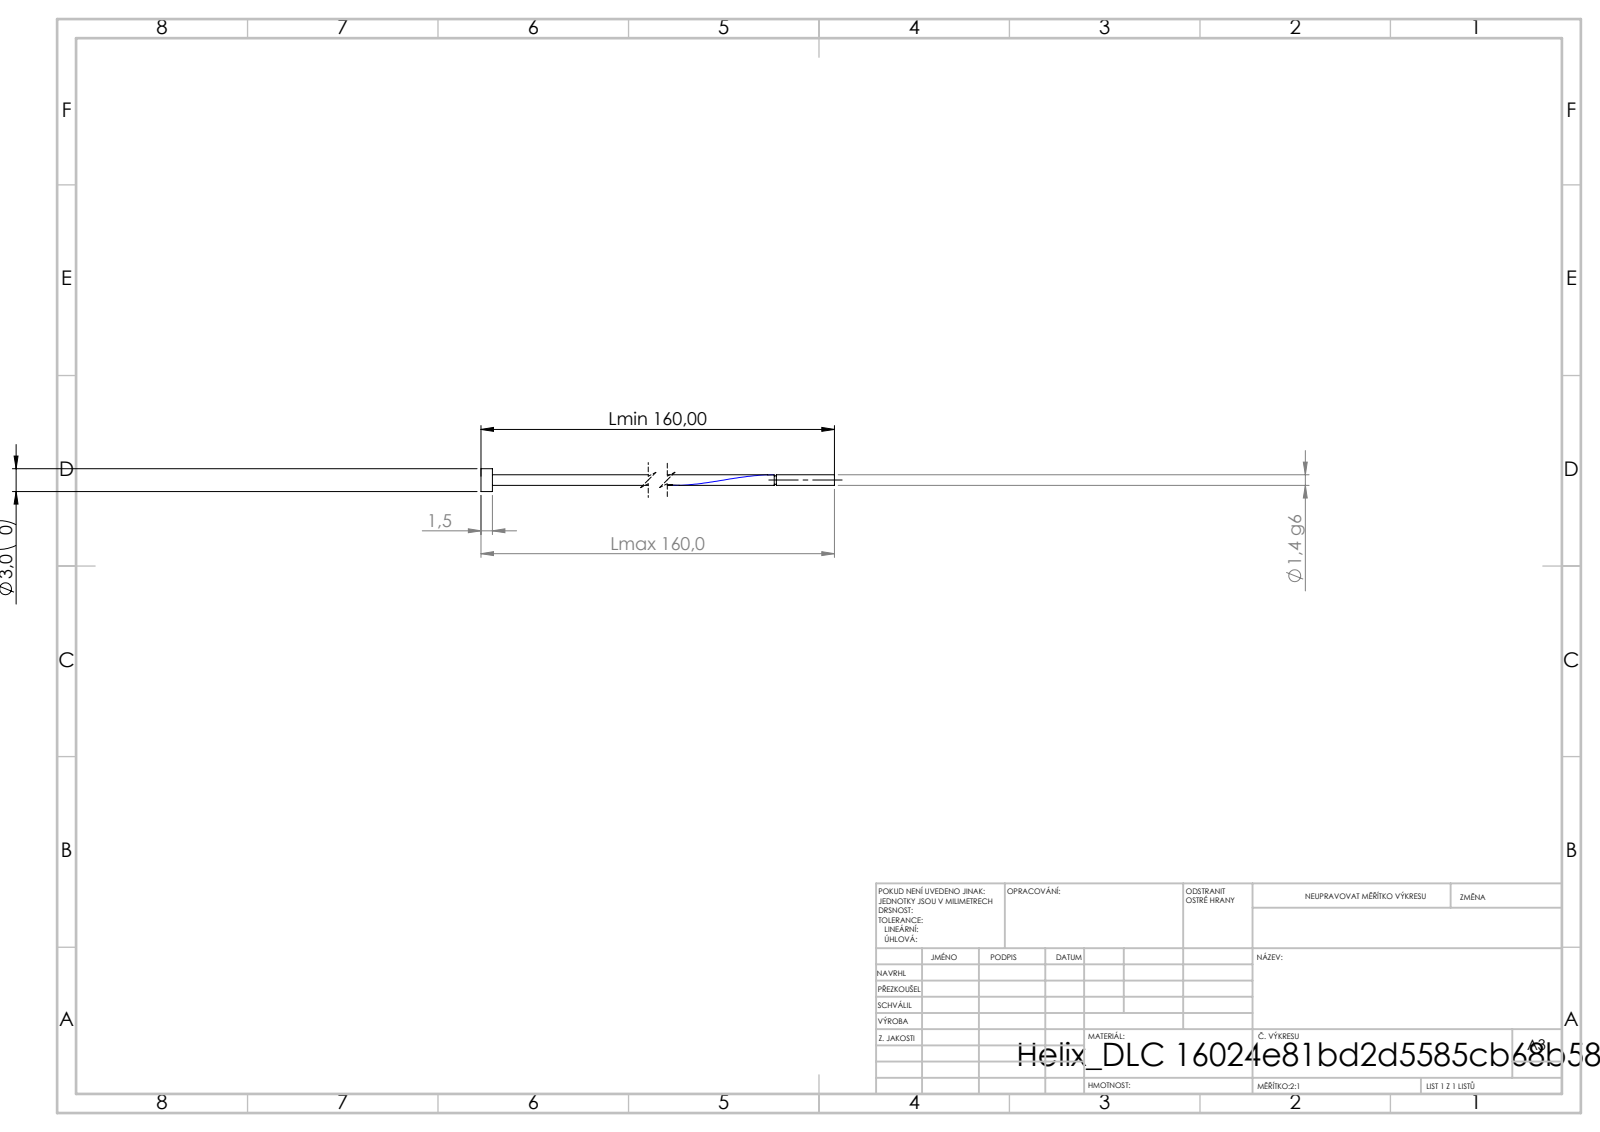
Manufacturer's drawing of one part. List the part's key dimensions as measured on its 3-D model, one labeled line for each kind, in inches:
STEP written by: SolidWorks 2019 (CONFIG_CONTROL_DESIGN)
Units: inches
Bodies: 1 solid, 16 faces (6 planar, 9 cylindrical, 1 other)
Overall size (bounding box): 6.299 × 0.118 × 0.118
Volume: 0.019 in³ · Surface area: 1.51 in²
Round bosses / shafts (diameter × count): ⌀0.118 ×1, ⌀0.055 ×1, ⌀0.044 ×1
Main face-to-face distances: 0.059, 6.299, 6.24, 5.999, 5.94, 0.3, 5.988, 5.929, 0.311, 2.839
